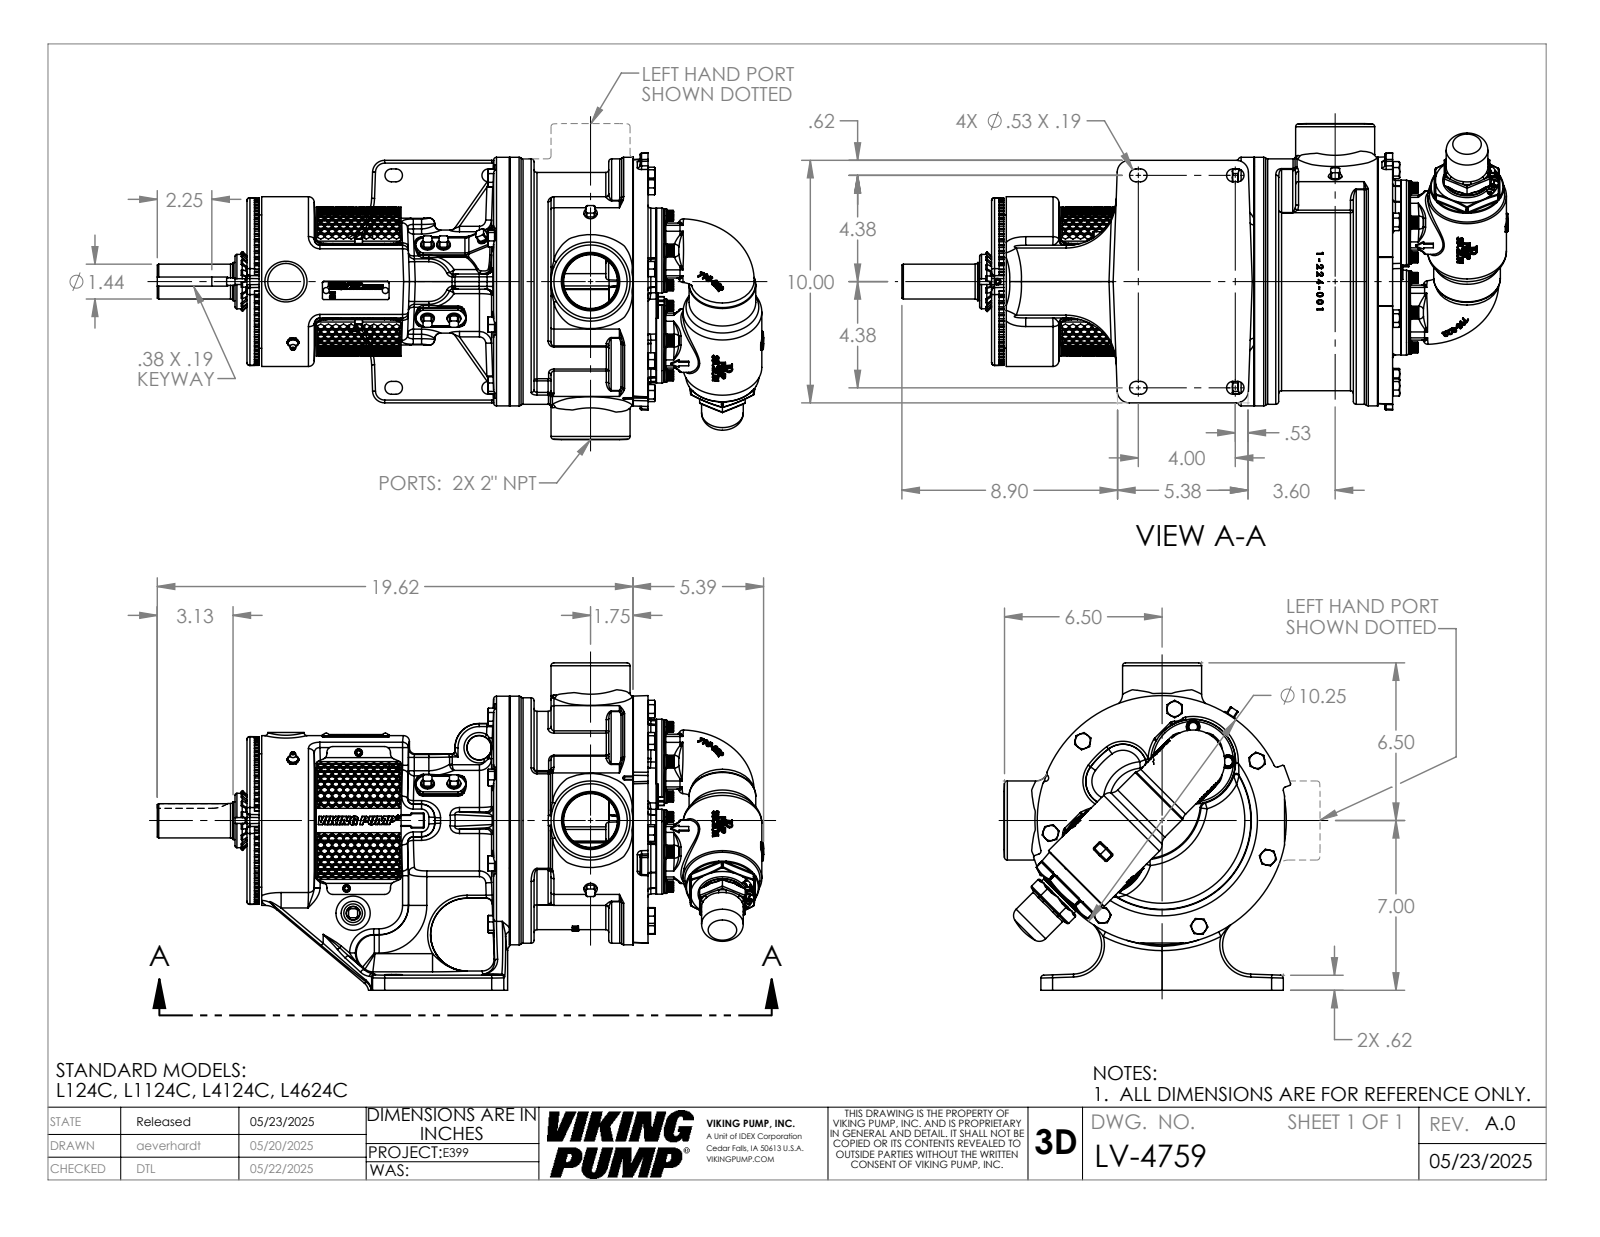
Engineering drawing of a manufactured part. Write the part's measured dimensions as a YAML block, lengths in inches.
part_name: "LV-4759"
step_written_by: "SolidWorks 2024 (AUTOMOTIVE_DESIGN)"
units: inches
bodies: {solids: 1, faces: 5286, planar: 1744, cylindrical: 1116, other: 2426}
overall_size: [25.01, 13.5, 11.817]
volume: 843.7
surface_area: 1270
round_holes:
  - {diameter: 0.406, count: 8}
  - {diameter: 0.41, count: 8}
  - {diameter: 1.094, count: 8}
  - {diameter: 0.199, count: 6}
  - {diameter: 0.25, count: 6}
  - {diameter: 0.159, count: 3}
  - {diameter: 0.266, count: 2}
  - {diameter: 0.313, count: 2}
  - {diameter: 0.453, count: 1}
  - {diameter: 1.552, count: 1}
  - {diameter: 1.577, count: 1}
  - {diameter: 1.593, count: 1}
round_bosses_or_shafts:
  - {diameter: 0.625, count: 8}
  - {diameter: 0.563, count: 8}
  - {diameter: 0.625, count: 7}
  - {diameter: 0.375, count: 5}
  - {diameter: 3.5, count: 3}
  - {diameter: 0.437, count: 3}
  - {diameter: 0.375, count: 3}
  - {diameter: 0.312, count: 3}
partial_cylinders:
  - {radius: 0.063, count: 109}
  - {radius: 0.12, count: 84}
  - {radius: 0.069, count: 74}
  - {radius: 0.24, count: 48}
  - {radius: 0.03, count: 38}
  - {radius: 0.45, count: 16}
  - {radius: 0.06, count: 13}
  - {radius: 0.25, count: 12}
face_to_face_distances: [13.792, 3.537, 10.255, 0.5, 2.25, 2.143, 5.68, 15.935, 0.607, 2.75]
hole_center_spacings: [3, 1.375, 3.609, 1.709, 2.18, 2.249, 4.089, 4.446]
